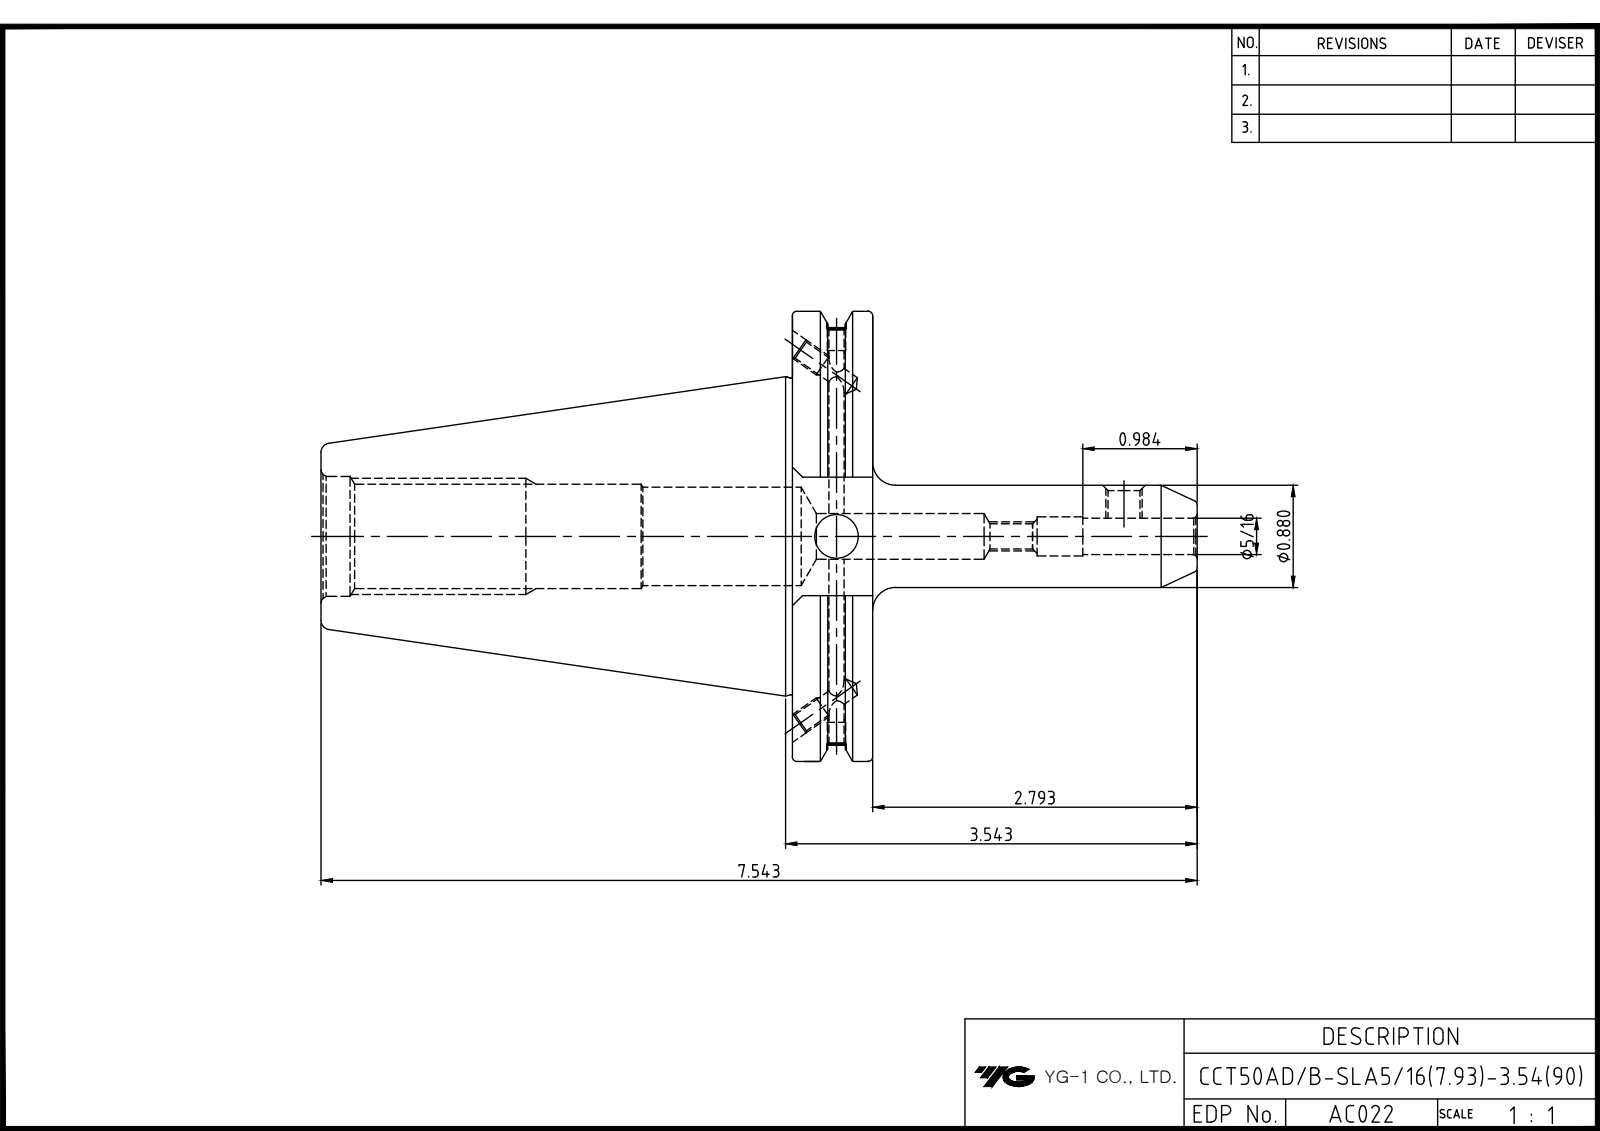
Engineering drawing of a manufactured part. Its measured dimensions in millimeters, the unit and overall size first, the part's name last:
Units: millimetres
Overall size (bounding box): 191.6 × 98.42 × 94.69
Round holes (diameter × count): ⌀3.24 ×2, ⌀4.13 ×2, ⌀4.2 ×2, ⌀5 ×2, ⌀5.36 ×1, ⌀6.78 ×1, ⌀7.94 ×1, ⌀9.14 ×1, ⌀9.53 ×1, ⌀10 ×1, ⌀21.97 ×1, ⌀26.2 ×1
Round bosses / shafts (diameter × count): ⌀98.42 ×1, ⌀91.29 ×1, ⌀69.25 ×1, ⌀22.35 ×1
Main face-to-face distances: 17.55, 103.1, 120.65, 73.03, 25.9, 103.5, 0.4, 17.15, 114.64, 11.54
Volume: 350 142 mm³ · Surface area: 51 720 mm²
Bodies: 1 solid, 92 faces (39 planar, 28 cylindrical, 25 other)
Part name (STEP PRODUCT): LO-CCT50ADB-SLA7.9375-90
STEP written by: Autodesk Inventor 2025 (AUTOMOTIVE_DESIGN)
